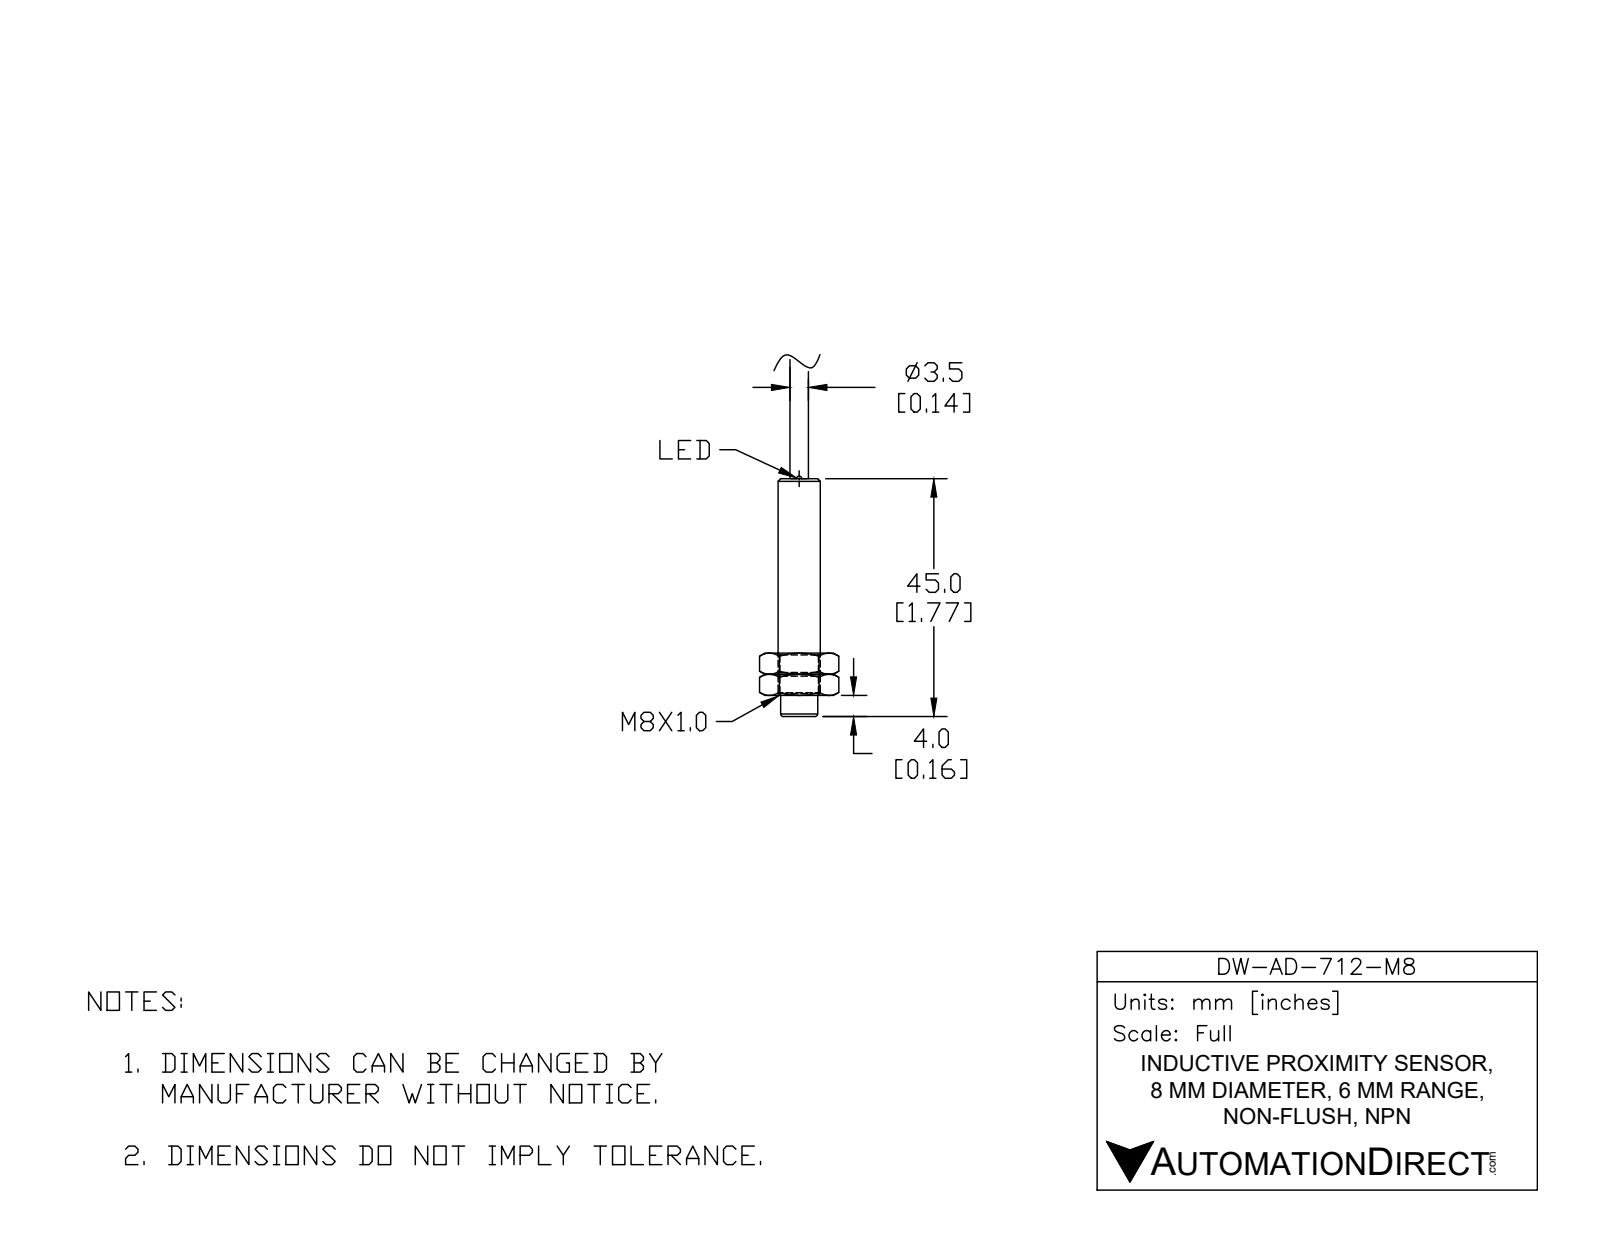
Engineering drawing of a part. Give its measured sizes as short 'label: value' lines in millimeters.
name: DW-AD-712-M8
written by: SolidWorks 2017 (AUTOMOTIVE_DESIGN)
unit: mm
bodies: 2 solids, 9 faces (4 planar, 3 cylindrical, 2 other)
size: 65 × 8 × 8
volume: 2 410 mm³; area: 1 443 mm²
bosses: 1× ⌀8, 1× ⌀7, 1× ⌀3.5
face distances: 45, 20, 65
